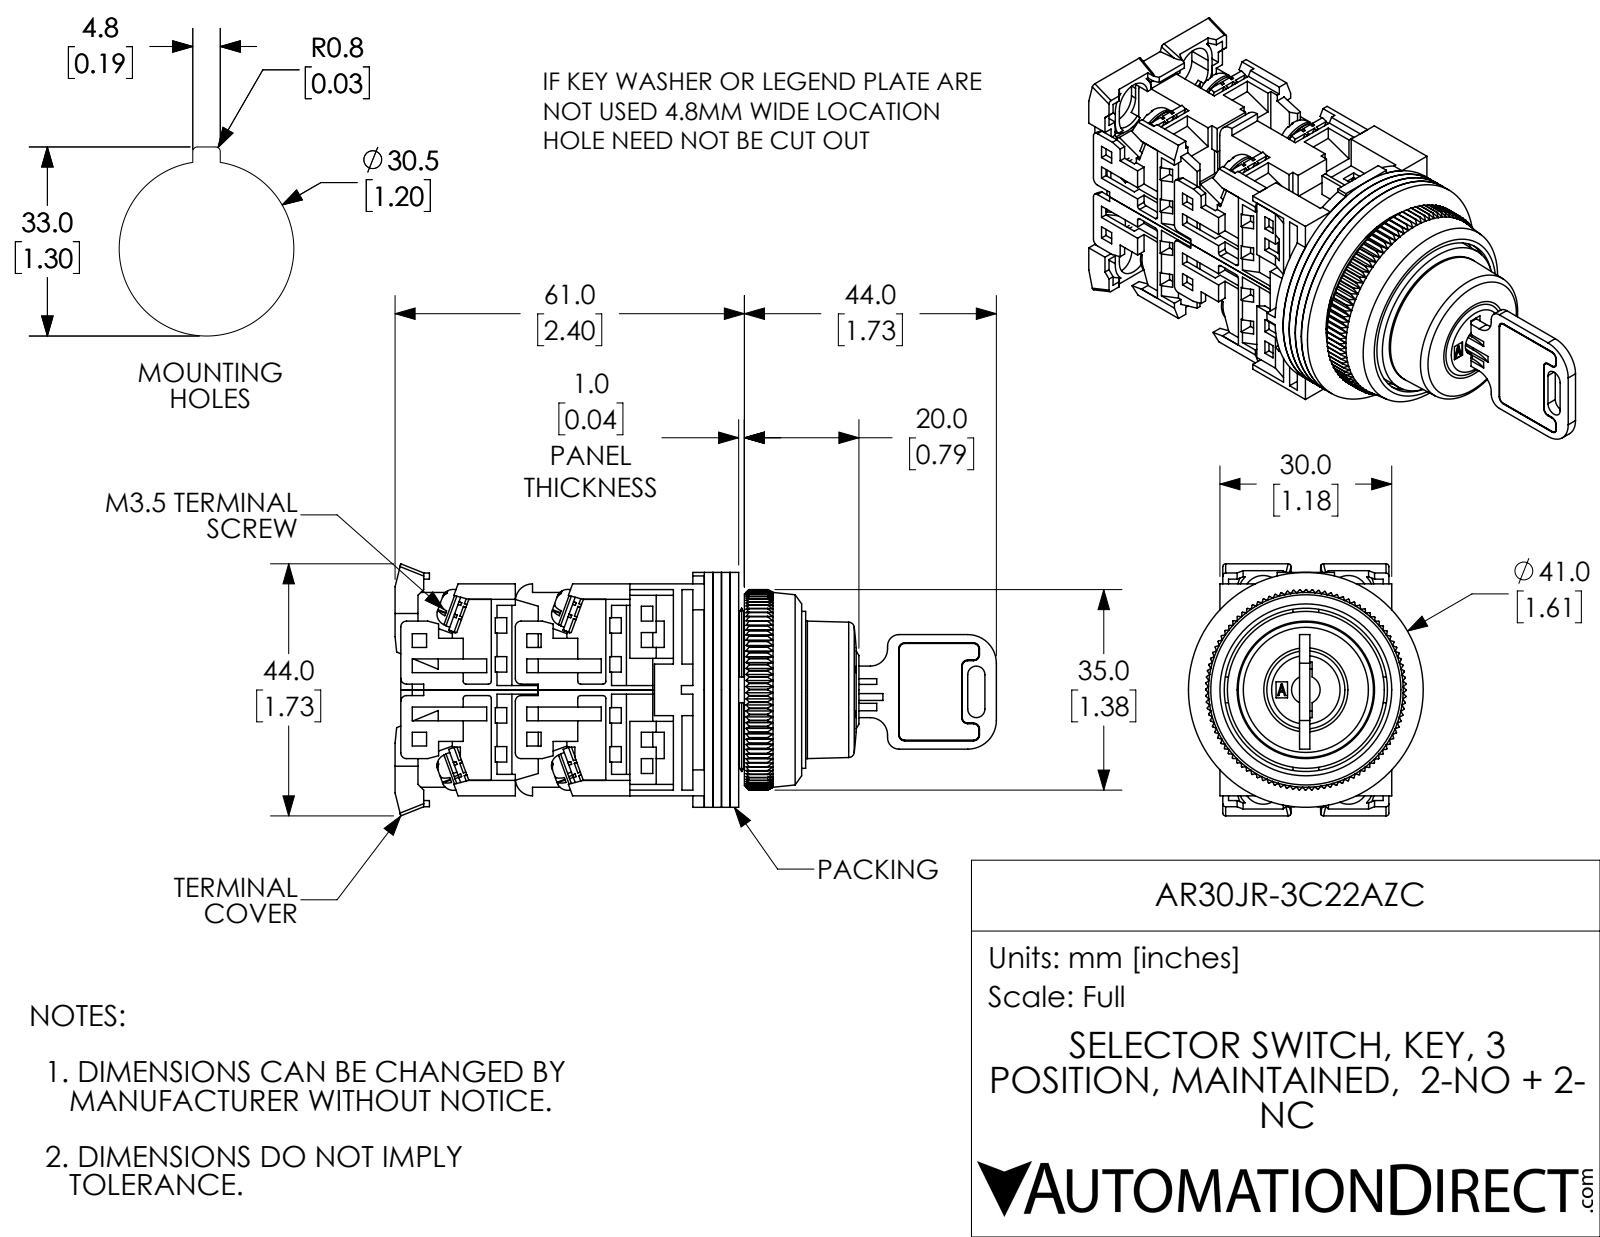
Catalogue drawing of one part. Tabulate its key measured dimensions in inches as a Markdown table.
| quantity | value |
| --- | --- |
| part name | AR30JR-3C22AZC |
| STEP written by | SolidWorks 2017 (AUTOMOTIVE_DESIGN) |
| units | inches |
| bodies | 38 solids, 2546 faces (1941 planar, 325 cylindrical, 280 other) |
| overall size | 4.134 × 1.732 × 1.614 |
| volume | 3.32 in³ |
| surface area | 69.28 in² |
| round holes (diameter × count) | 0.138 × 12, 0.142 × 8, 0.118 × 1, 0.709 × 1, 0.945 × 1, 1.122 × 1, 1.181 × 1, 1.252 × 1 |
| round bosses / shafts (diameter × count) | 0.26 × 8, 0.138 × 8, 1.614 × 1, 1.15 × 1, 1.079 × 1 |
| partial cylindrical surfaces (radius × count) | 0.059 × 34, 0.02 × 16, 0.039 × 9, 0.118 × 6, 0.008 × 4, 0.138 × 4, 0.177 × 4, 0.079 × 2 |
| main face-to-face distances | 0.059, 0.118, 0.039, 0.787, 0.079, 0.177, 0.063, 0.138, 0.02, 0.256 |
| hole center spacings | 0.579, 0.269, 0.638, 0.61 |
